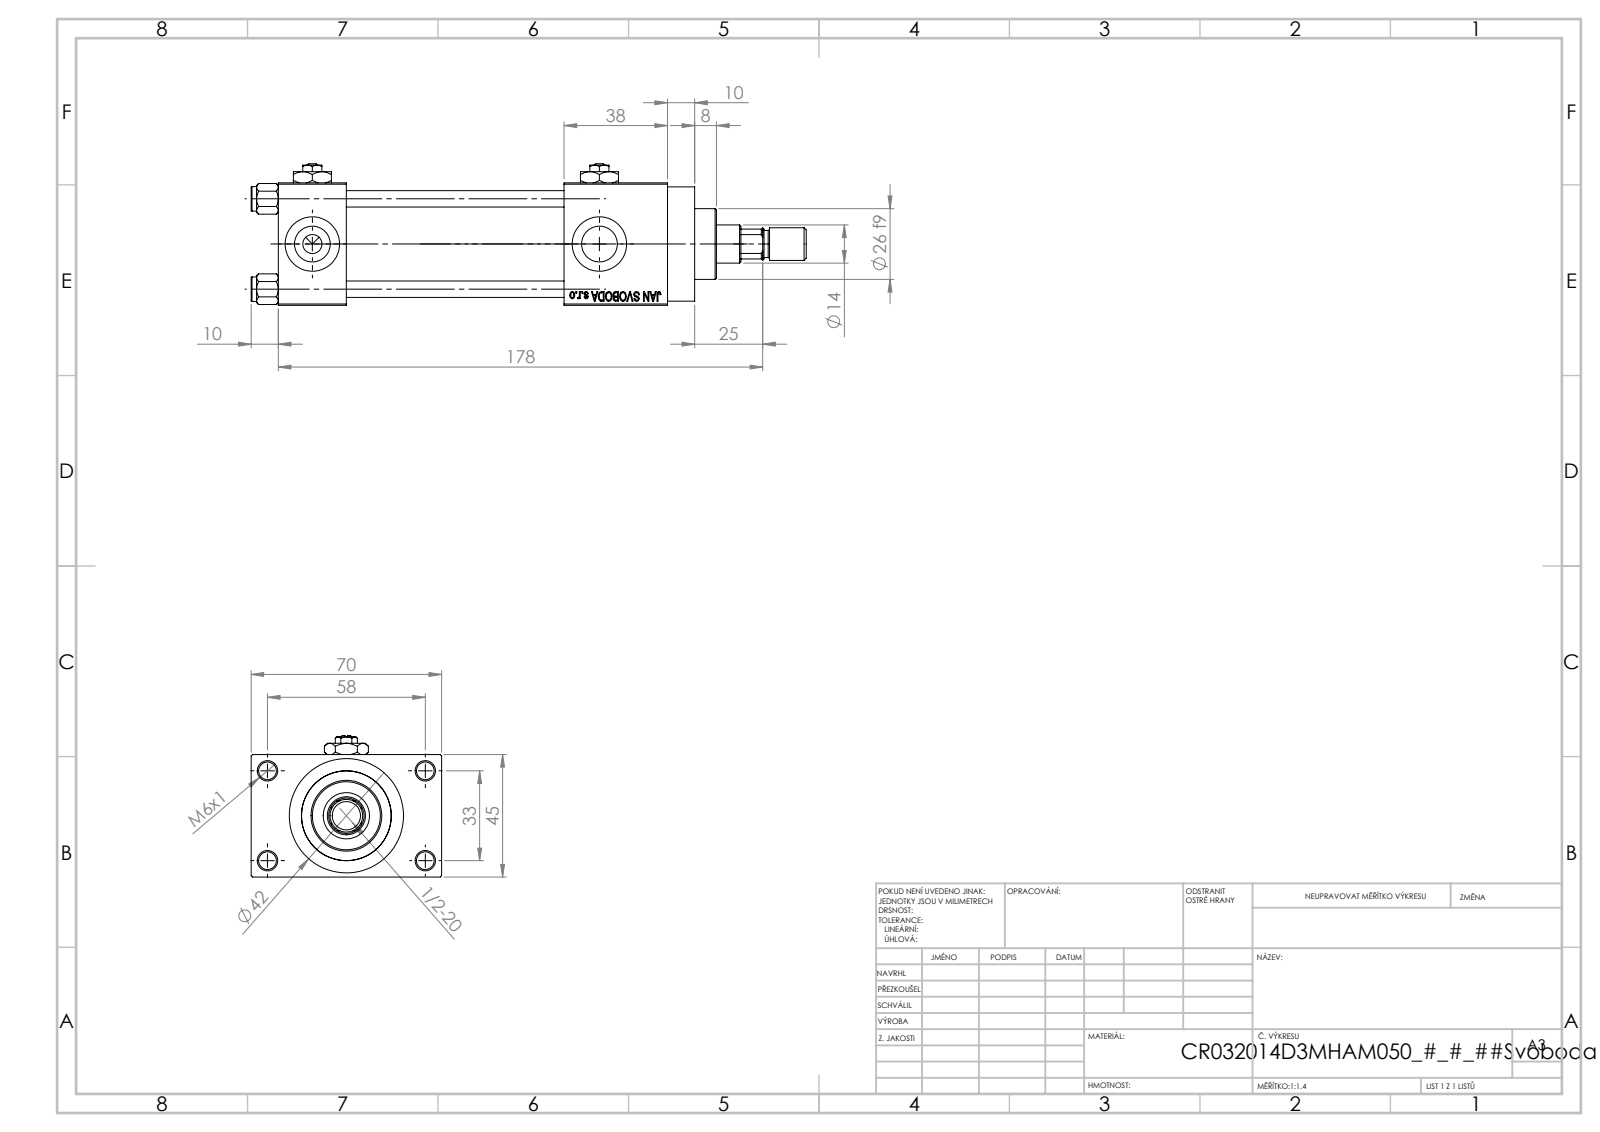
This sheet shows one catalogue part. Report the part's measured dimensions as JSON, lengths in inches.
{"part_name": "NUT_M5_D; V215_VC_A; ROD_END_AH; V215CR_D_TYCINKA (+3 more)", "step_written_by": "SolidWorks 2019 (CONFIG_CONTROL_DESIGN)", "units": "inches", "bodies": {"solids": 14, "faces": 1215, "planar": 546, "cylindrical": 103, "other": 566}, "overall_size": [8.031, 2.756, 2.047], "volume_in3": 15.18, "surface_area_in2": 136.6, "round_holes": [[0.256, 5], [0.236, 4], [0.518, 4], [0.787, 4], [0.276, 3], [0.551, 1], [0.669, 1], [0.945, 1], [1.26, 1], [1.299, 1]], "round_bosses_or_shafts": [[0.354, 4], [1.654, 1], [1.496, 1], [1.024, 1], [0.472, 1], [0.394, 1]], "partial_cylinders_radius": [[0.256, 1]], "face_to_face_distances": [1.772, 0.984, 0.492, 3.15, 4.134, 2.264, 4.646, 1.496, 5.63, 2.756], "hole_center_spacings": [0.488, 0.924, 1.307, 1.314, 1.392, 1.795, 2.219, 1.299]}
